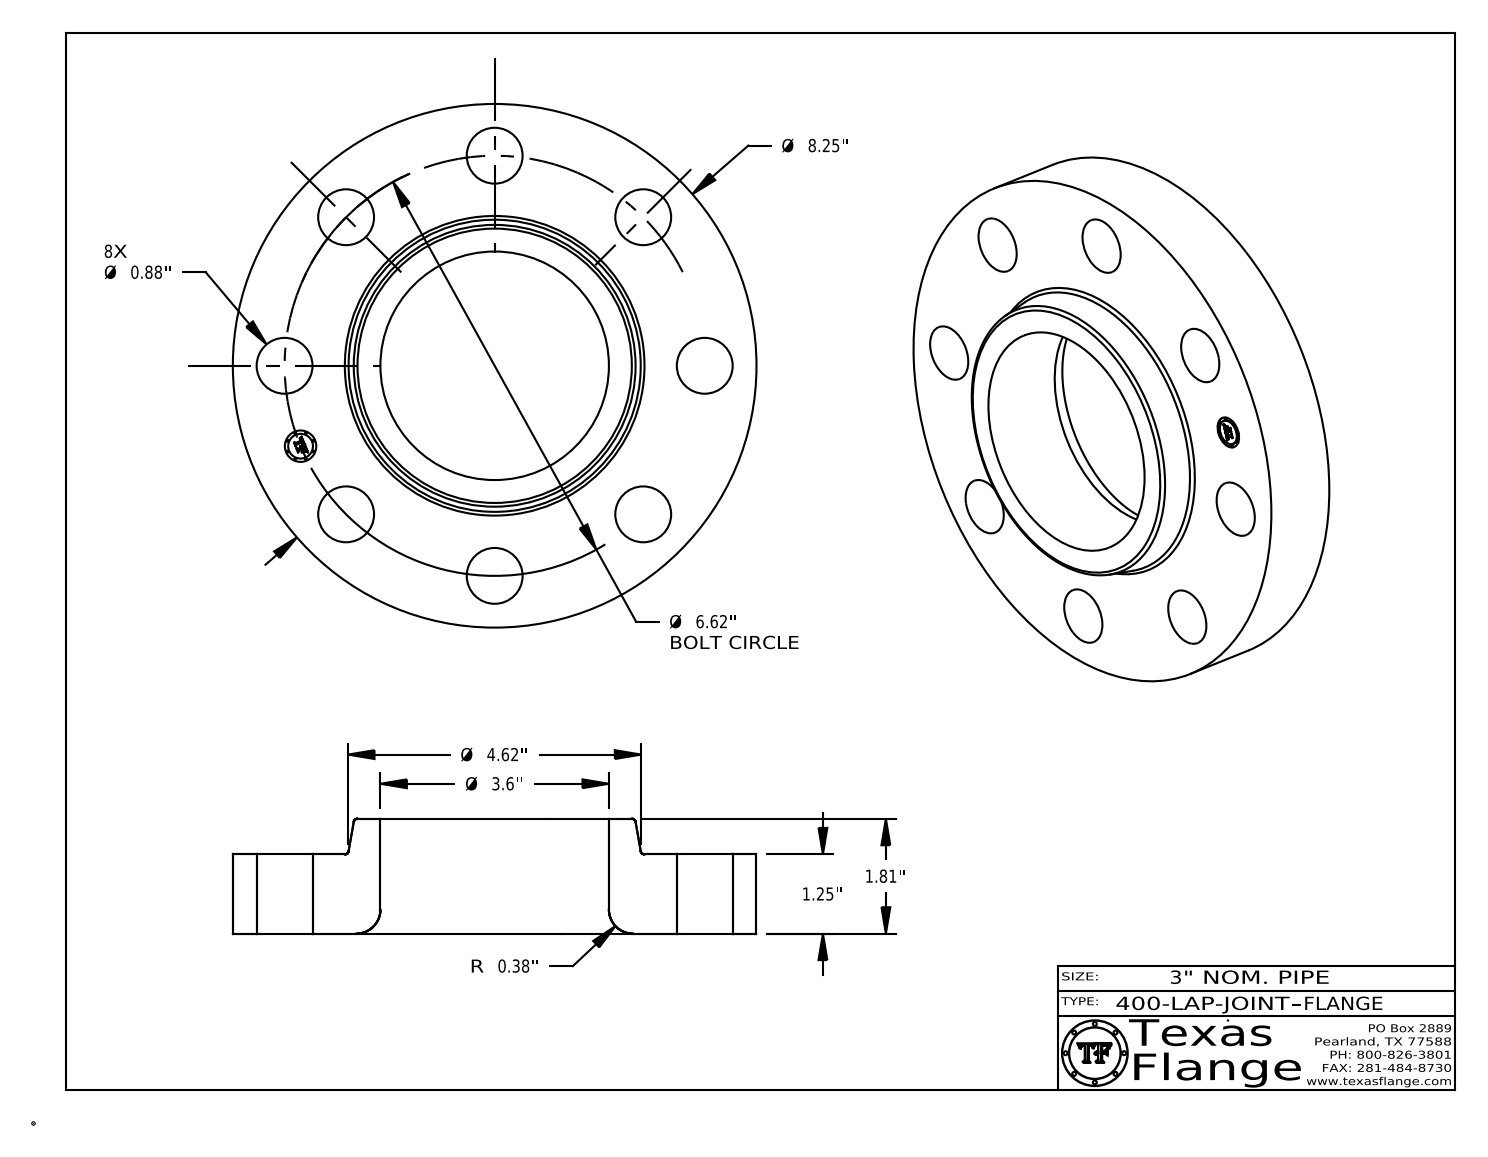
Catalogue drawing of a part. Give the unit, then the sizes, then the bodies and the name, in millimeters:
Units: millimetres
Overall size (bounding box): 209.6 × 209.6 × 46
Round holes (diameter × count): ⌀22.4 ×8, ⌀12.6 ×1, ⌀91.4 ×1
Round bosses / shafts (diameter × count): ⌀0.8 ×8, ⌀209.6 ×1, ⌀9.9 ×1
Main face-to-face distances: 31.8, 46, 14.2, 0.4, 31.4, 14.6, 3.8, 3.7, 0.7, 2.4
Hole centre spacings: 84.1, 64.3, 155.3, 118.9, 118.9, 32.8, 93.4, 164.9
Volume: 834 800 mm³ · Surface area: 104 400 mm²
Bodies: 1 solid, 416 faces (368 planar, 40 cylindrical, 8 other)
Part name (STEP PRODUCT): 400-LAP-JOINT FLANGE
STEP written by: CATIA V5 STEP AP214 (AUTOMOTIVE_DESIGN)
